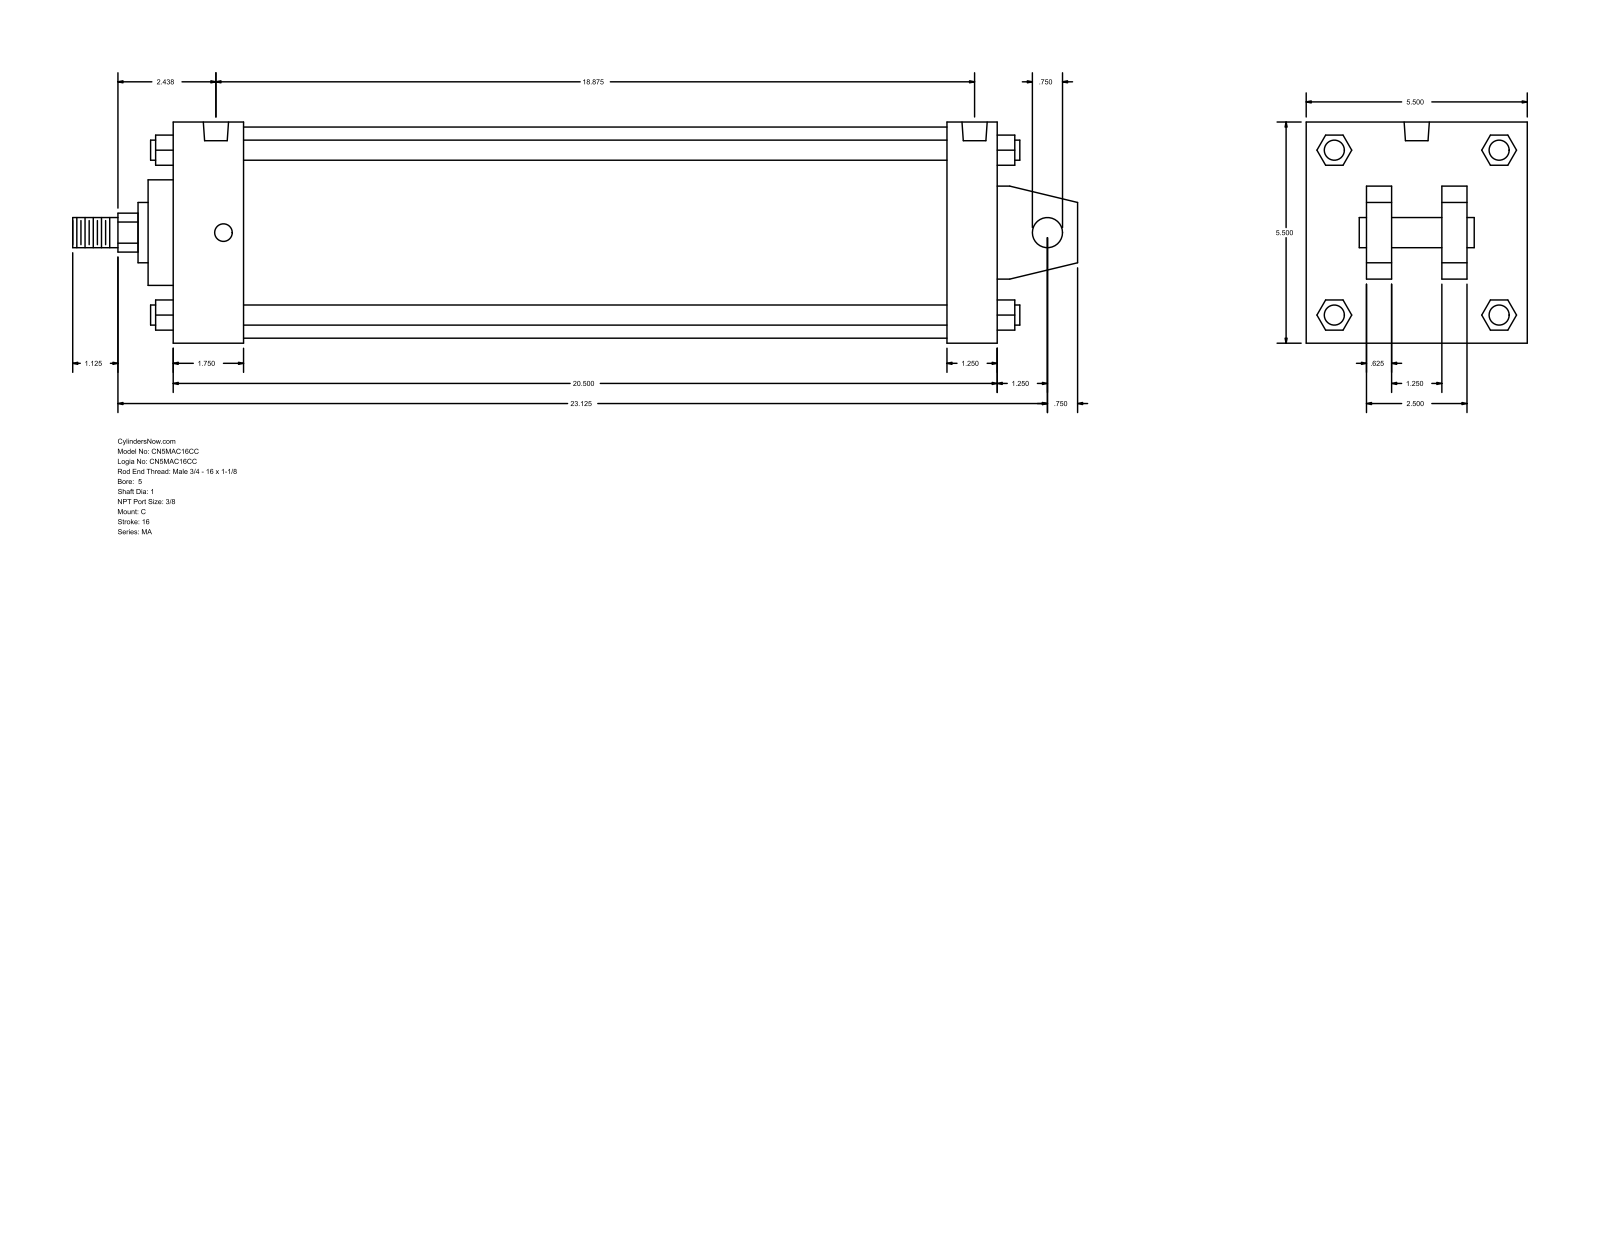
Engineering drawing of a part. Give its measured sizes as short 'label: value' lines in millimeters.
name: MA_C__0500_1
written by: GSSL Pune (CONFIG_CONTROL_DESIGN)
unit: mm
bodies: 0 solids, 141 faces (109 planar, 32 cylindrical, 0 other)
size: 635 × 139.7 × 139.7
holes: 4× ⌀11.11, 2× ⌀15.93
bosses: 4× ⌀12.7, 2× ⌀19.05, 1× ⌀133.35, 1× ⌀66.67, 1× ⌀38.1, 1× ⌀25.4
rounds: 1× R12.29
face distances: 139.7, 520.7, 15.87, 488.96, 31.74, 44.46, 444.5, 476.24, 38.1, 101.6
hole spacings: 4.76, 469.91, 474.67, 479.43
